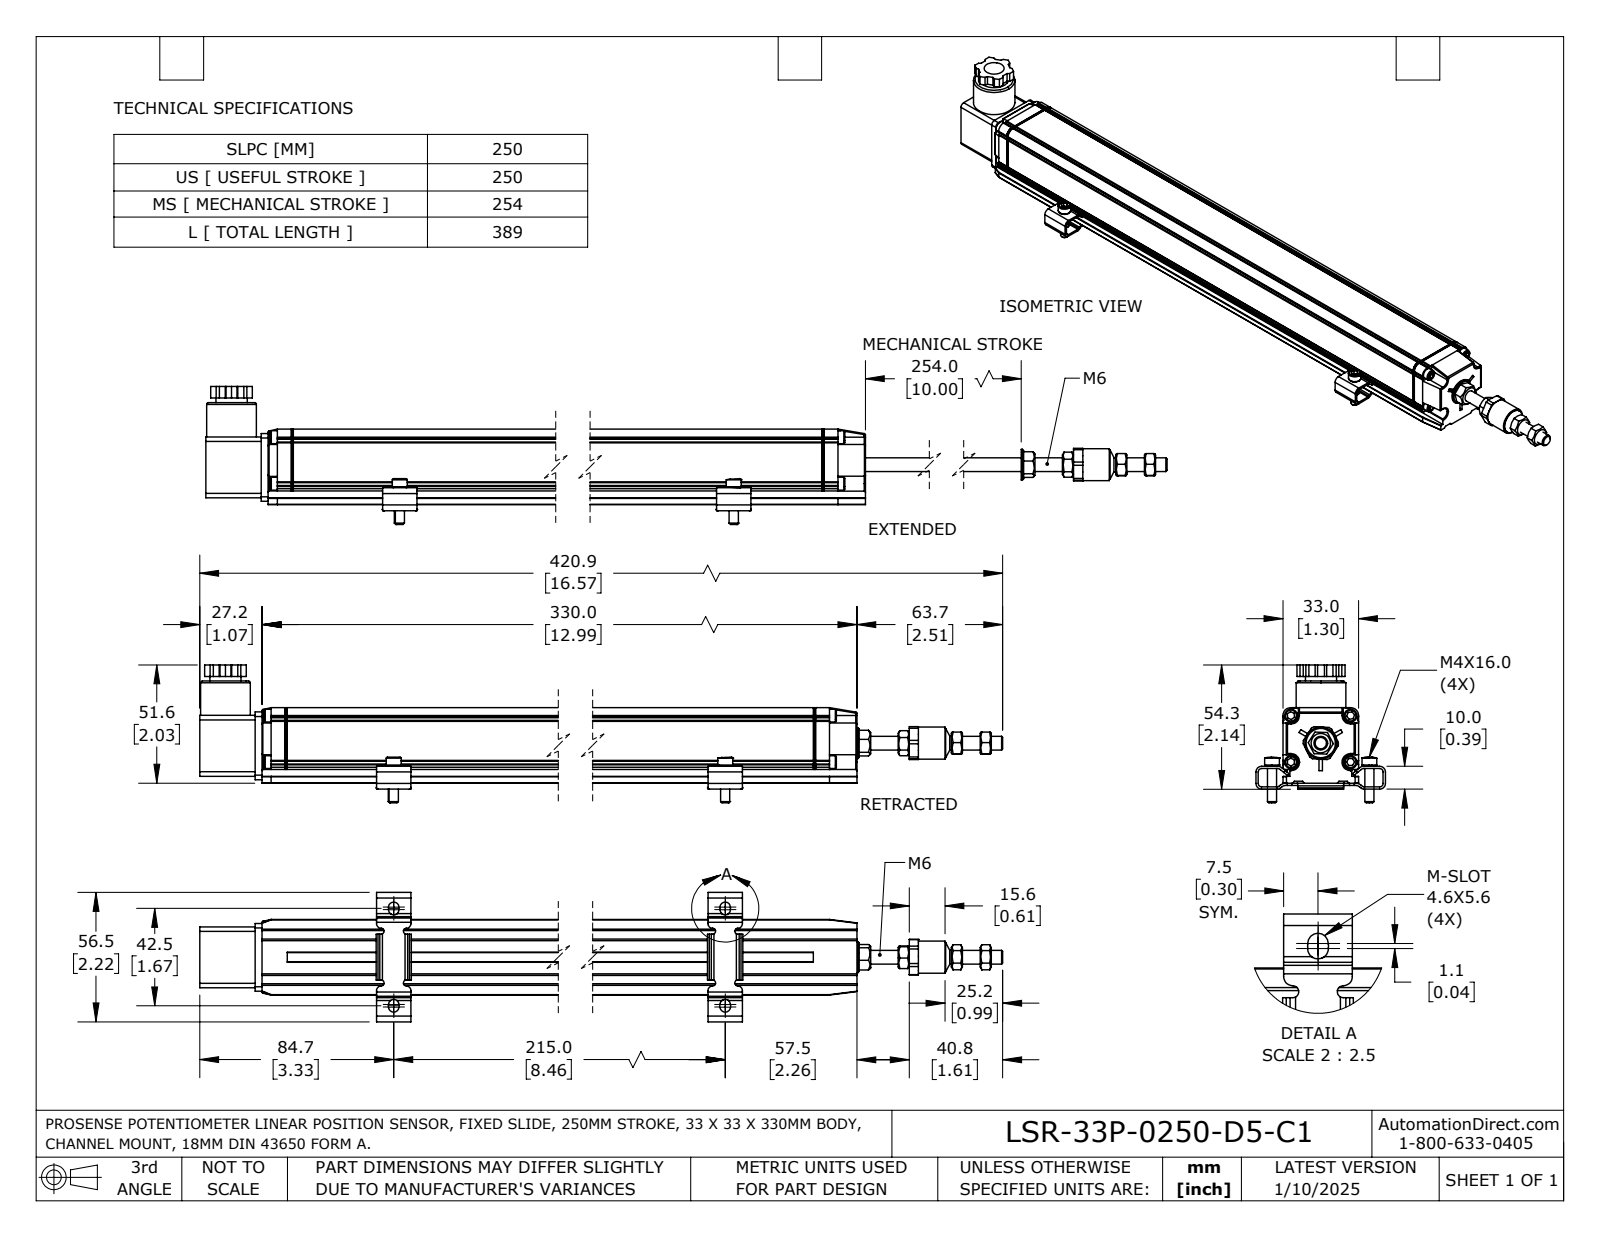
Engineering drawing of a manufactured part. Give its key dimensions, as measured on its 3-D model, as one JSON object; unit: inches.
{"part_name": "LSR-33P-0250-D5-C1", "step_written_by": "SolidWorks 2023 (AUTOMOTIVE_DESIGN)", "units": "inches", "bodies": {"solids": 14, "faces": 995, "planar": 641, "cylindrical": 269, "other": 85}, "overall_size": [16.569, 2.37, 2.224], "volume_in3": 20.95, "surface_area_in2": 146, "round_holes": [[0.106, 4], [0.13, 4], [0.169, 1], [0.205, 1], [0.209, 1], [0.232, 1], [0.276, 1], [0.285, 1], [0.394, 1], [0.413, 1], [0.573, 1], [0.602, 1]], "round_bosses_or_shafts": [[0.157, 5], [0.118, 5], [0.256, 4], [0.22, 4], [0.854, 1], [0.551, 1], [0.535, 1], [0.528, 1]], "partial_cylinders_radius": [[0.079, 28], [0.02, 23], [0.008, 16], [0.051, 8], [0.059, 8], [0.089, 8], [0.118, 8], [0.039, 4]], "face_to_face_distances": [1.299, 0.118, 0.039, 0.22, 1.181, 1.079, 0.079, 0.102, 0.142, 0.185], "hole_center_spacings": [0.047, 0.583, 0.607, 0.696, 0.73, 0.799, 1.024, 1.299]}
